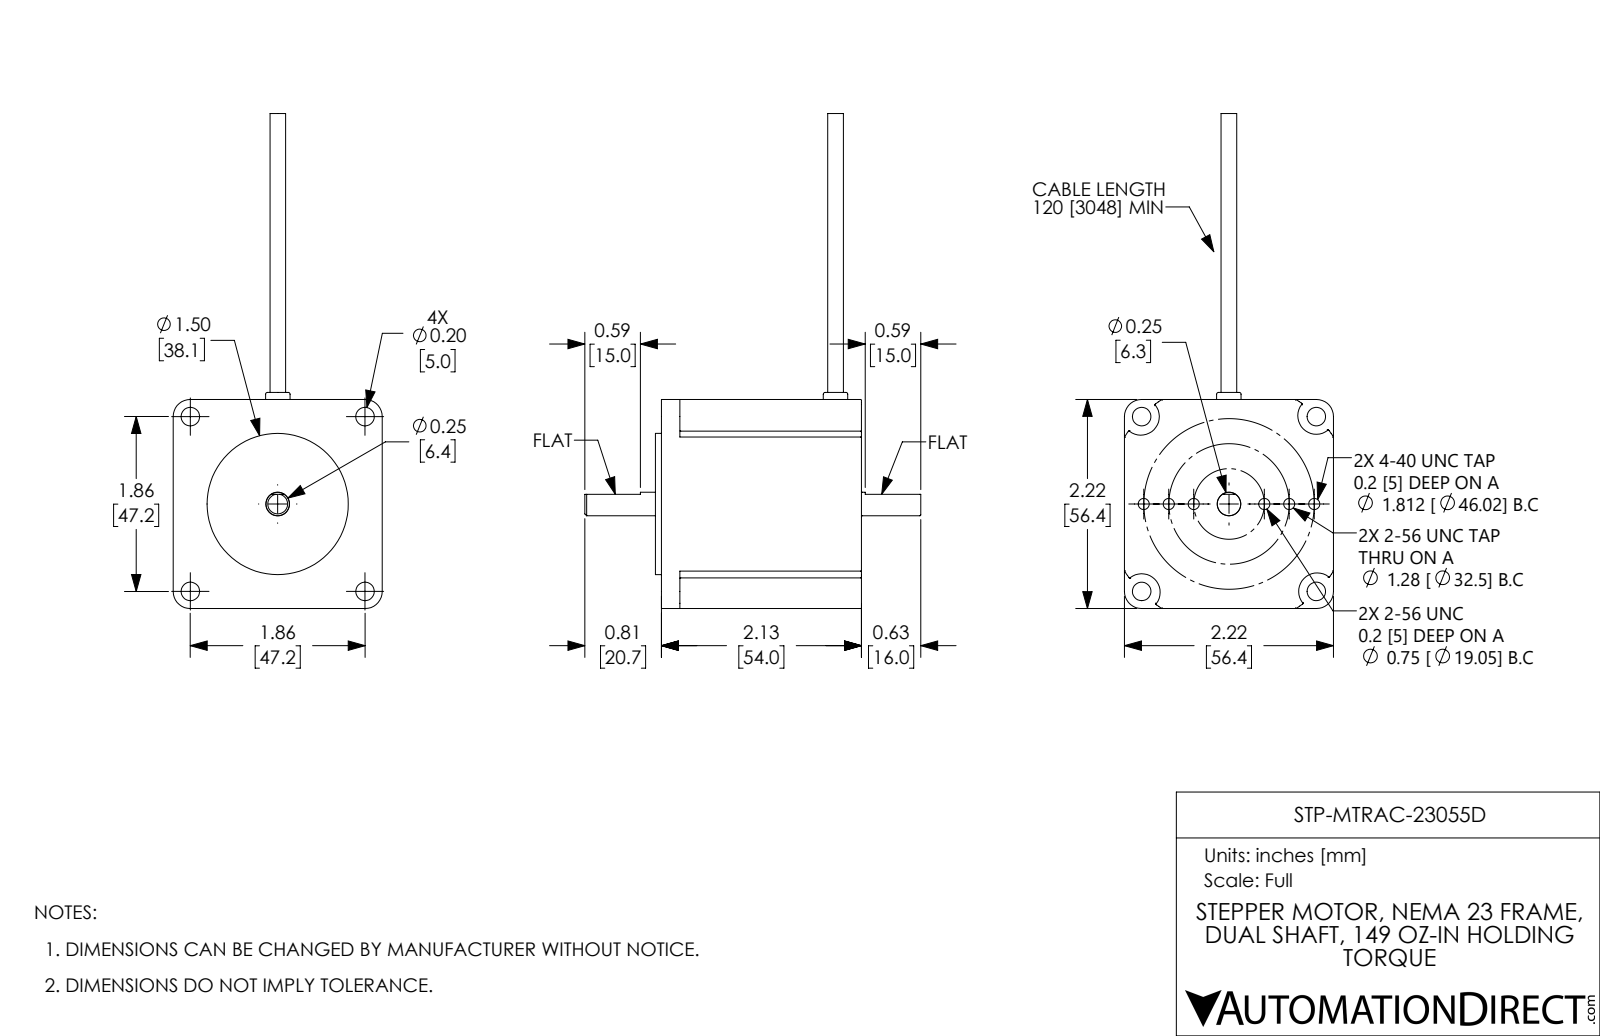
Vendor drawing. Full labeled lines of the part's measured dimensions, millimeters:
Part name (STEP PRODUCT): STP-MTRAC-23055D from HT23-553-CAA r1
STEP written by: SolidWorks 2017 (AUTOMOTIVE_DESIGN)
Units: millimetres
Bodies: 1 solid, 165 faces (25 planar, 62 cylindrical, 78 other)
Overall size (bounding box): 133.5 × 90.65 × 56.4
Volume: 159 045 mm³ · Surface area: 20 575 mm²
Round holes (diameter × count): ⌀3 ×6, ⌀5 ×4
Round bosses / shafts (diameter × count): ⌀38.1 ×1, ⌀6.58 ×1, ⌀6.35 ×1, ⌀4.23 ×1
Partial cylindrical surfaces — rounded edges, fillets, slot ends (radius × count): R0.25 ×12, R4.6 ×4, R5 ×4, R33.5 ×1
Main face-to-face distances: 56.4, 54, 55.6, 1.6, 5, 49, 6.6, 30.82, 25.58, 44
Hole centre spacings: 23.58, 24.68, 40.63, 46.27, 47.14, 52.2, 6.76, 27.43
